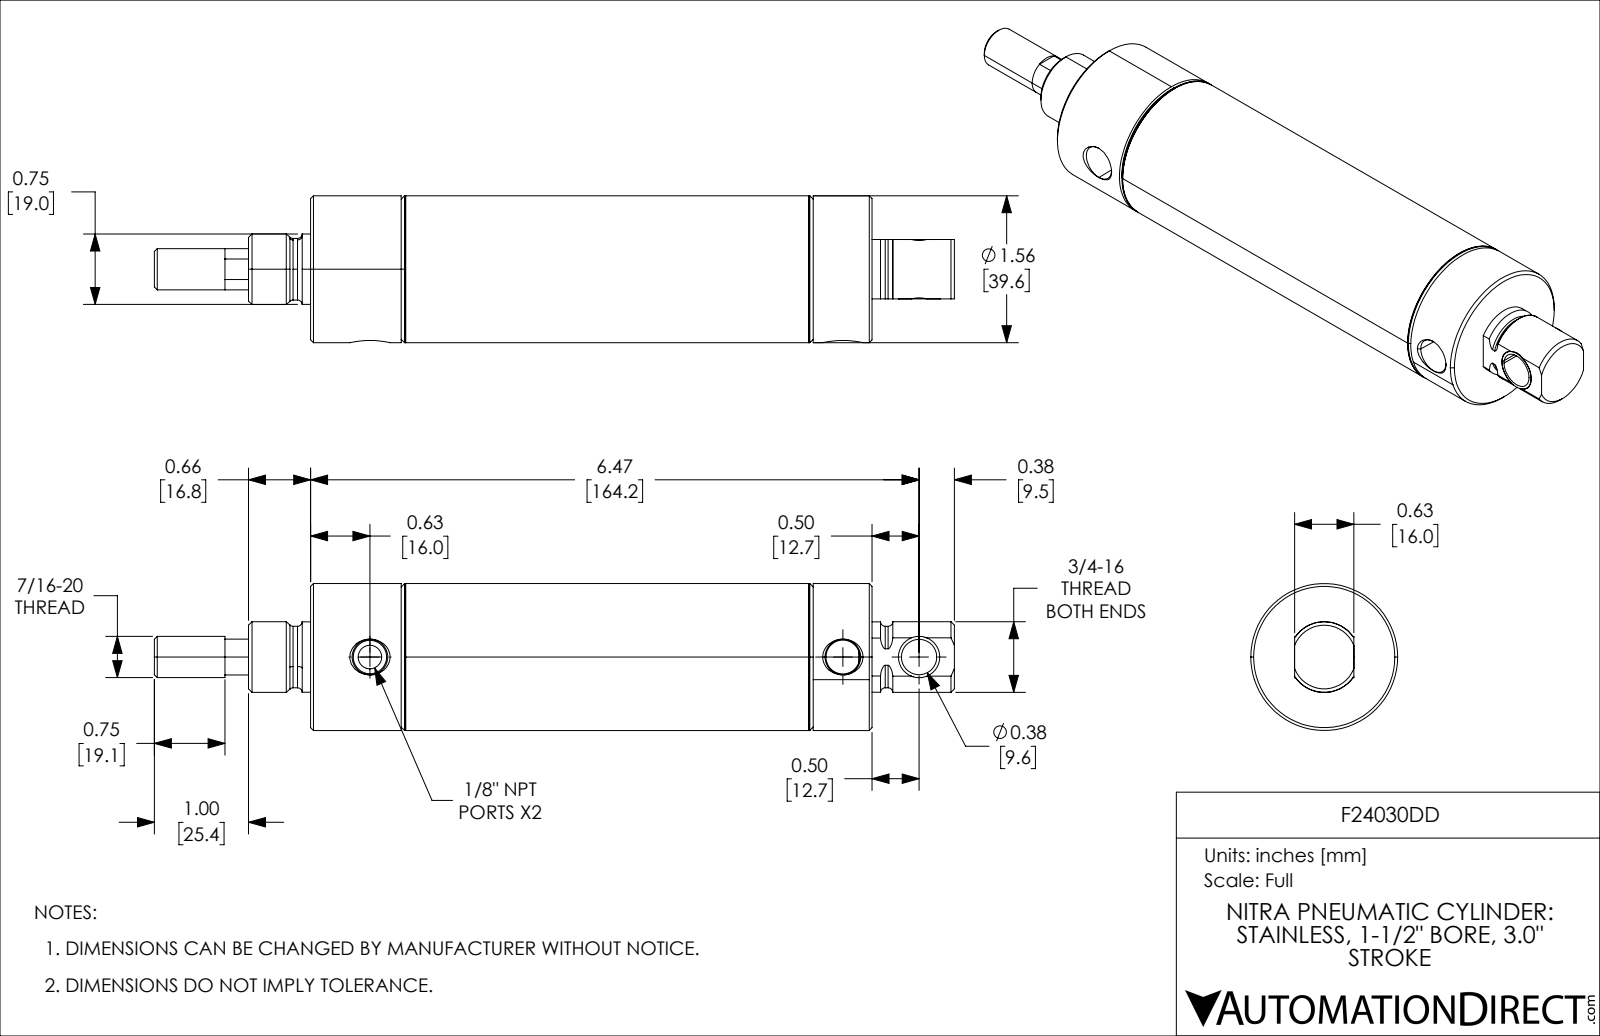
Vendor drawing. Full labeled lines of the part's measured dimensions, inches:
Part name (STEP PRODUCT): F24030DD_5; F24030DD; F24030DD_9; F24030DD_3 (+2 more)
STEP written by: SolidWorks 2021 (CONFIG_CONTROL_DESIGN)
Units: inches
Bodies: 5 solids, 157 faces (35 planar, 58 cylindrical, 64 other)
Overall size (bounding box): 8.5 × 1.56 × 1.56
Volume: 6.638 in³ · Surface area: 88.27 in²
Round holes (diameter × count): ⌀0.25 ×1, ⌀0.36 ×1, ⌀0.376 ×1, ⌀0.439 ×1, ⌀0.462 ×1, ⌀0.532 ×1, ⌀1.062 ×1, ⌀1.431 ×1
Round bosses / shafts (diameter × count): ⌀1.56 ×1, ⌀1.511 ×1, ⌀0.75 ×1, ⌀0.748 ×1, ⌀0.654 ×1, ⌀0.654 ×1, ⌀0.438 ×1, ⌀0.437 ×1
Main face-to-face distances: 0.875, 1.75, 3, 3.875, 4.75, 0.875, 1.215, 4.215, 5.09, 5.965
Hole centre spacings: 0.81, 5.025, 5.835
